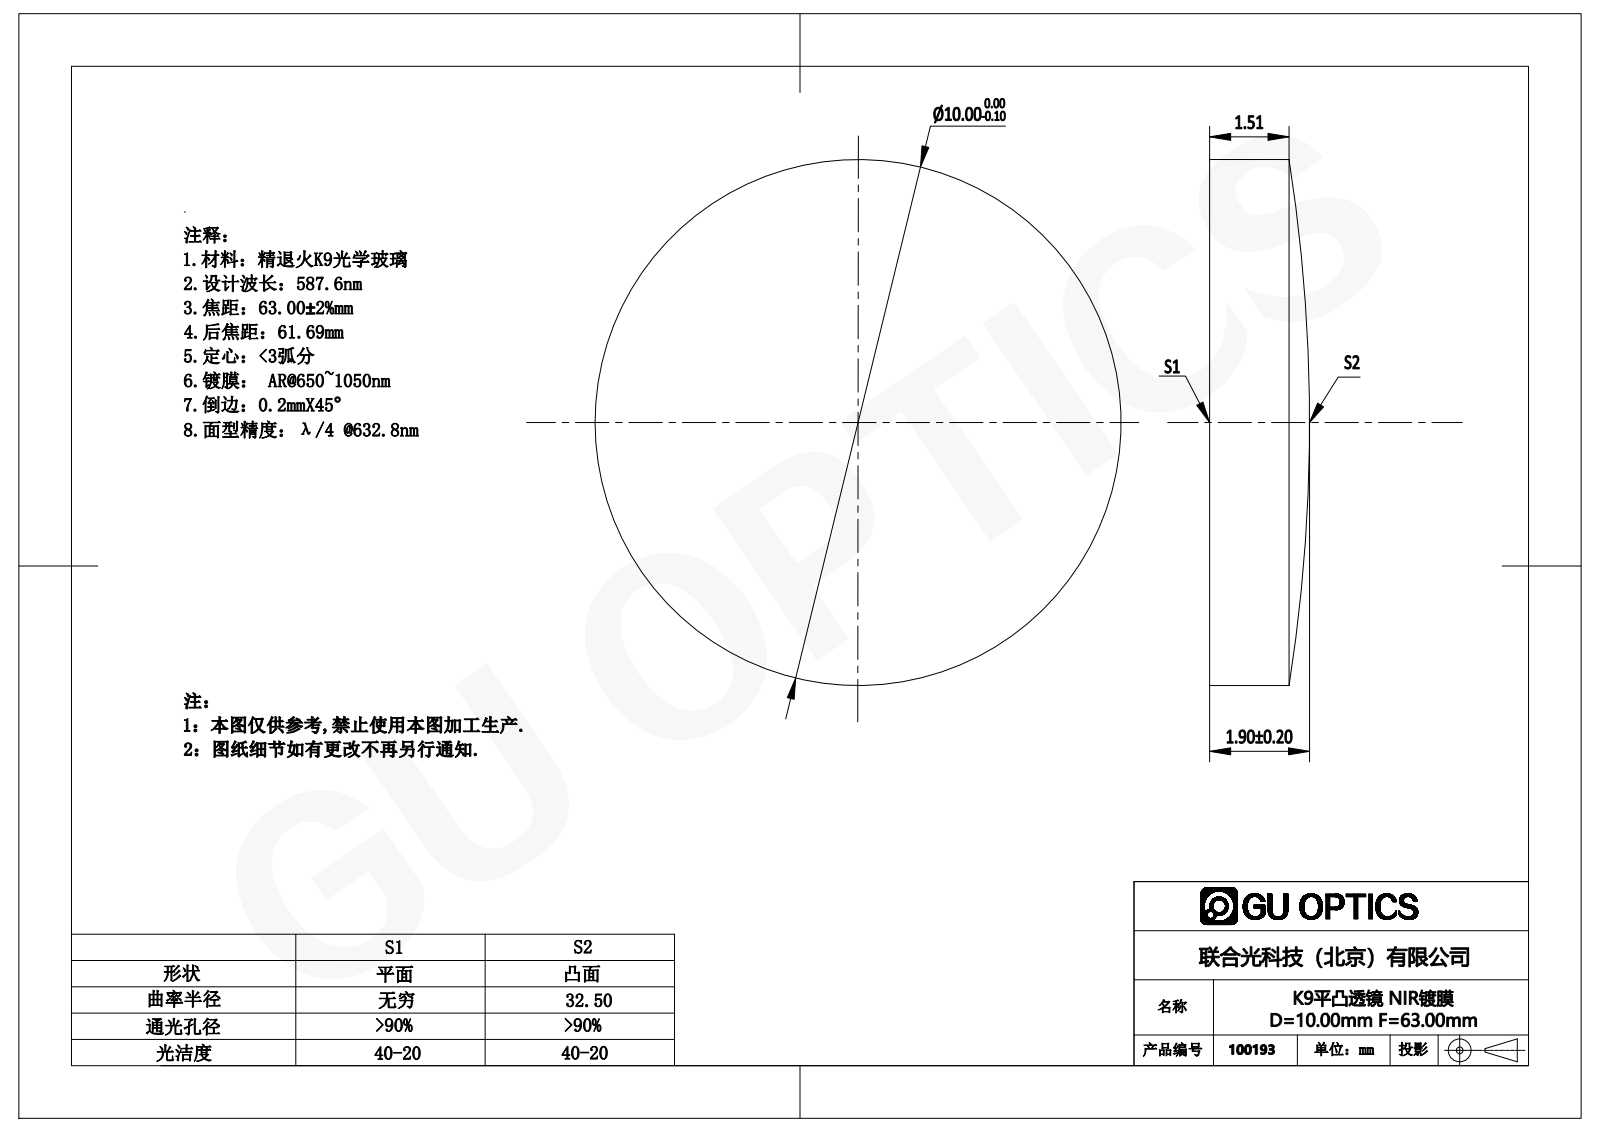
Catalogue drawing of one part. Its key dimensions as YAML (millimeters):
part_name: "100193"
step_written_by: "SolidWorks 2016 (AUTOMOTIVE_DESIGN)"
units: millimeters
bodies: {solids: 1, faces: 5, planar: 1, cylindrical: 2, other: 2}
overall_size: [10, 10, 1.9]
volume: 134
surface_area: 205
round_bosses_or_shafts:
  - {diameter: 10, count: 1}
